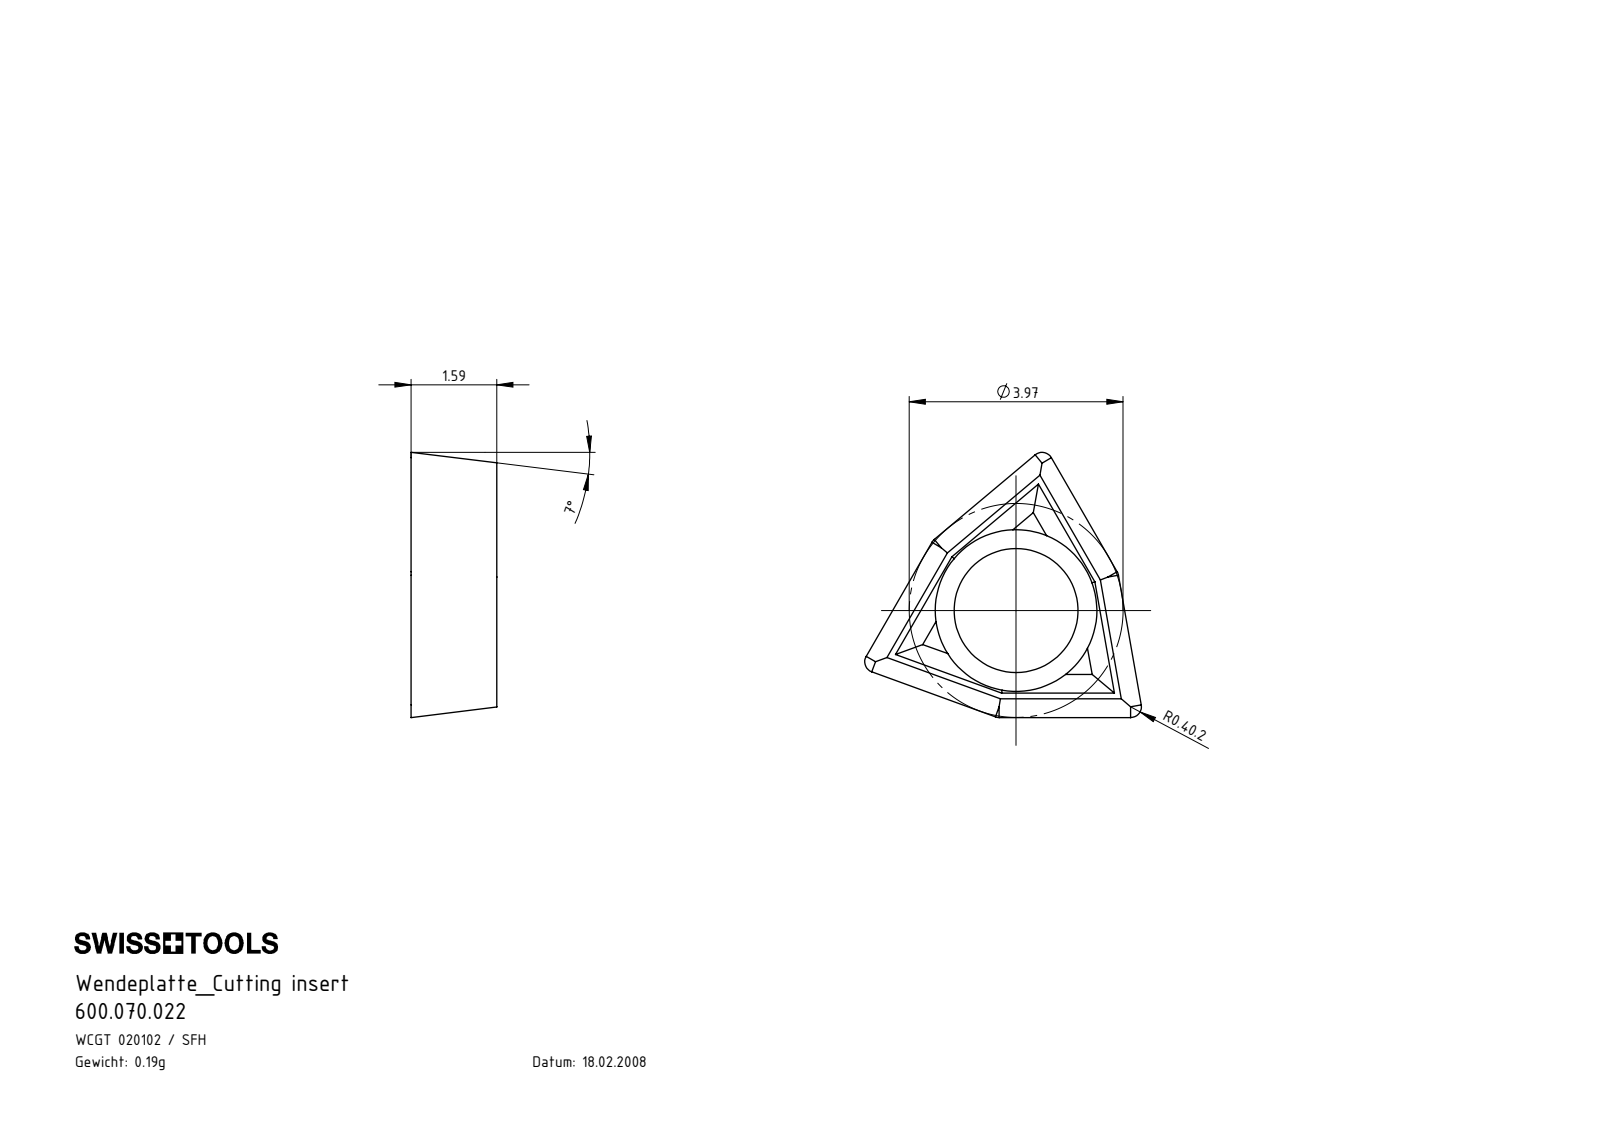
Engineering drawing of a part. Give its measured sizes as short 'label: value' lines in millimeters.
name: 600.070.022
written by: SolidWorks 2022 (AUTOMOTIVE_DESIGN)
unit: mm
bodies: 1 solid, 31 faces (14 planar, 5 cylindrical, 12 other)
size: 5.13 × 4.92 × 1.59
volume: 15 mm³; area: 56 mm²
holes: 1× ⌀2.3
rounds: 3× R0.3
face distances: 1.59
